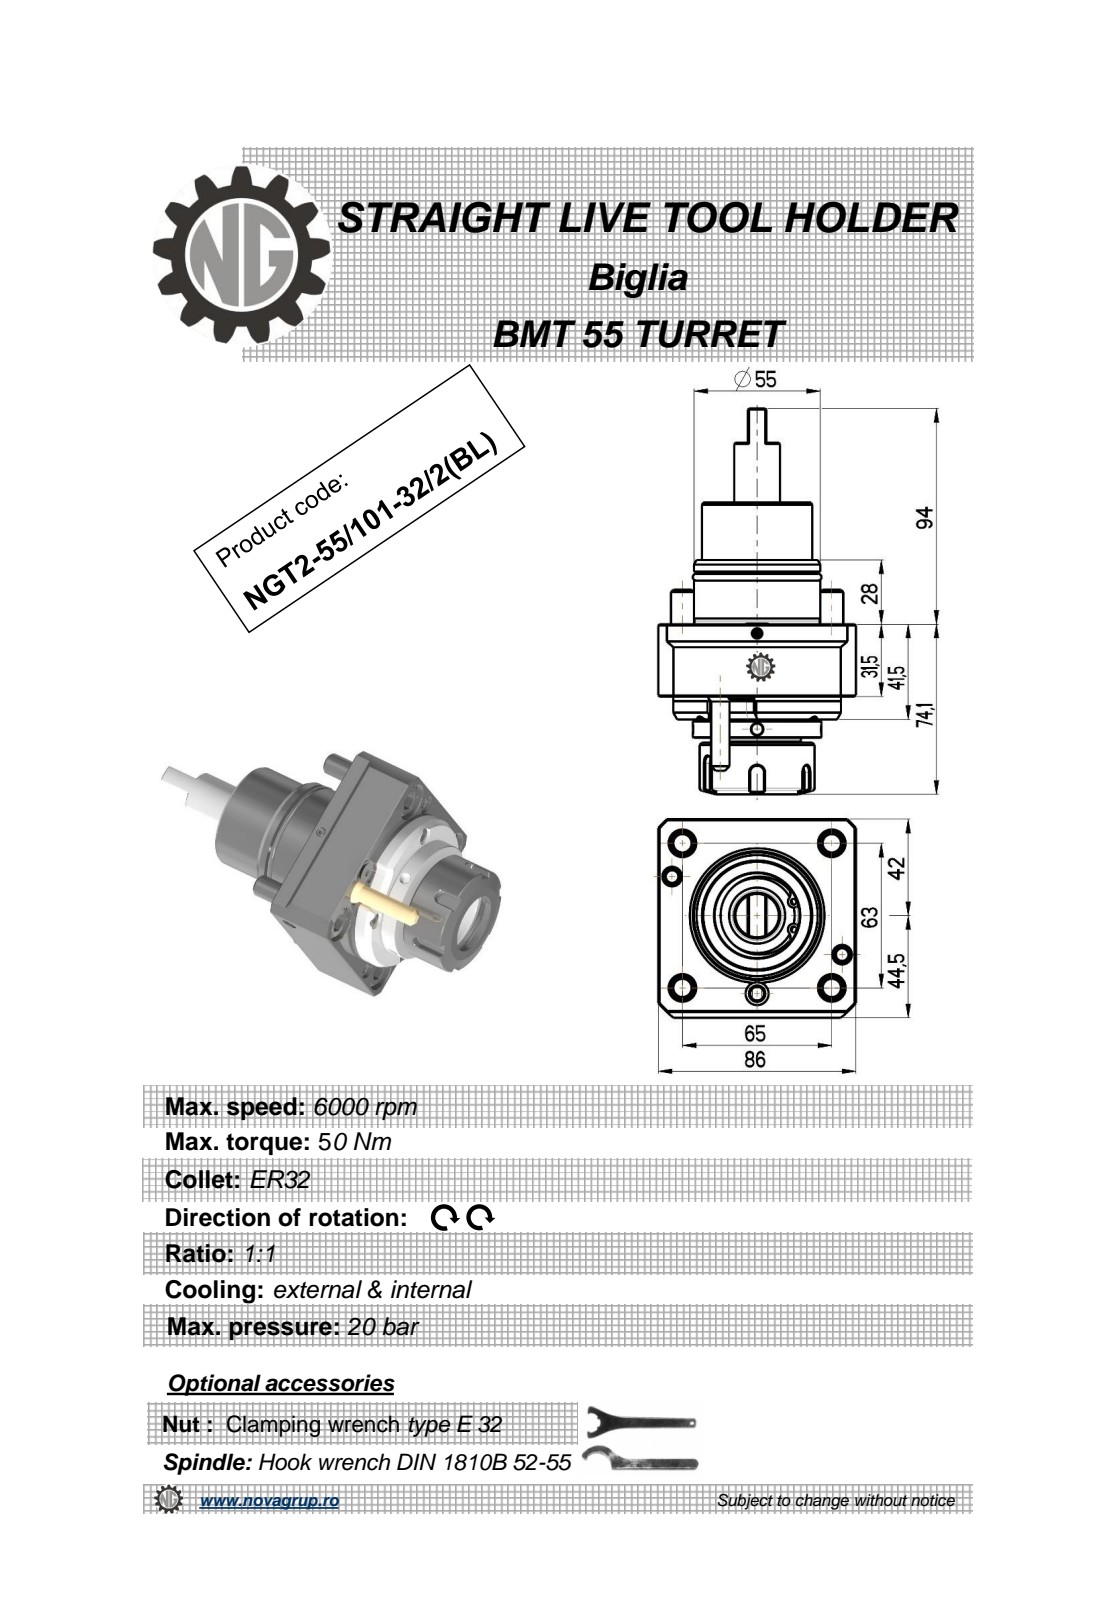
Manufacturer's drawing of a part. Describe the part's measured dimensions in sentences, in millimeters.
The part is named "NGT2_55_101_32_1_BL". Its 3-D file was written by "PRO/ENGINEER BY PARAMETRIC TECHNOLOGY CORPORATION, 2010280 (CONFIG_CONTROL_DESIGN)". It is 2 solids with 250 faces: 83 planar, 71 cylindrical and 96 other. Overall it measures 168.1 by 88.1 by 86 millimeters. Its volume is 459 306 cubic millimeters and its surface area 52 410 square millimeters. Round holes: 3 of diameter 5, 1 of diameter 3, 1 of diameter 6, 1 of diameter 27. Round bosses or shafts: 4 of diameter 10, 1 of diameter 73, 1 of diameter 56, 1 of diameter 55, 1 of diameter 54.4, 1 of diameter 50, 1 of diameter 48, 1 of diameter 44. Partial cylindrical surfaces (rounded edges, fillets, slot ends): 6 of radius 0.22, 5 of radius 3, 2 of radius 0.8, 2 of radius 6, 1 of radius 57.5. The main face-to-face distances are 31.5, 86, 41.5, 10, 86.5, 53, 84.5, 94.5, 18, 8. The hole center spacings are 16.01, 34, 37.12.
